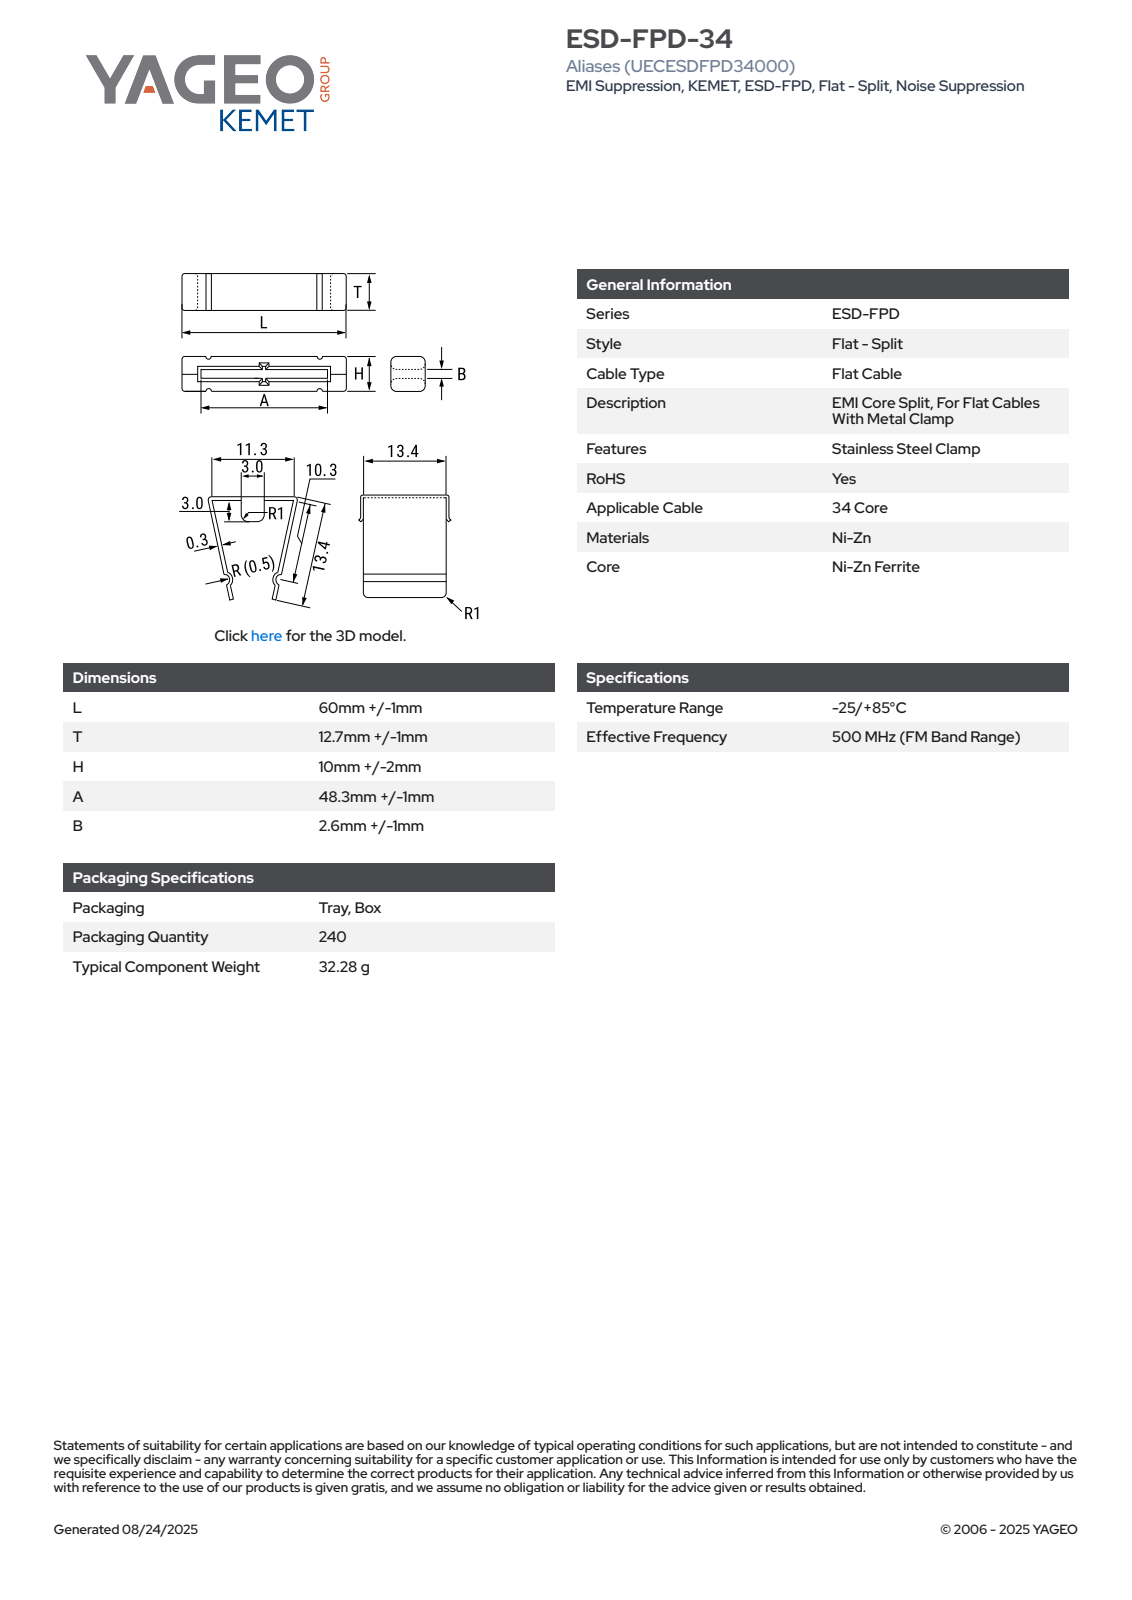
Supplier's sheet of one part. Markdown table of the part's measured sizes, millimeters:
| quantity | value |
| --- | --- |
| part name | EC_FPD_L61T13.7H12A48.3B2.6 |
| STEP written by | SolidWorks 2021 (AUTOMOTIVE_DESIGN) |
| units | millimeters |
| bodies | 4 solids, 91 faces (79 planar, 12 cylindrical, 0 other) |
| overall size | 61 × 12.7 × 12 |
| volume | 7 644 mm³ |
| surface area | 4 293 mm² |
| partial cylindrical surfaces (radius × count) | 0.5 × 8, 0.62 × 4 |
| main face-to-face distances | 4.7, 7.3, 12, 2.6, 12.7, 61, 16.76, 6.35, 54.65, 48.3 |
